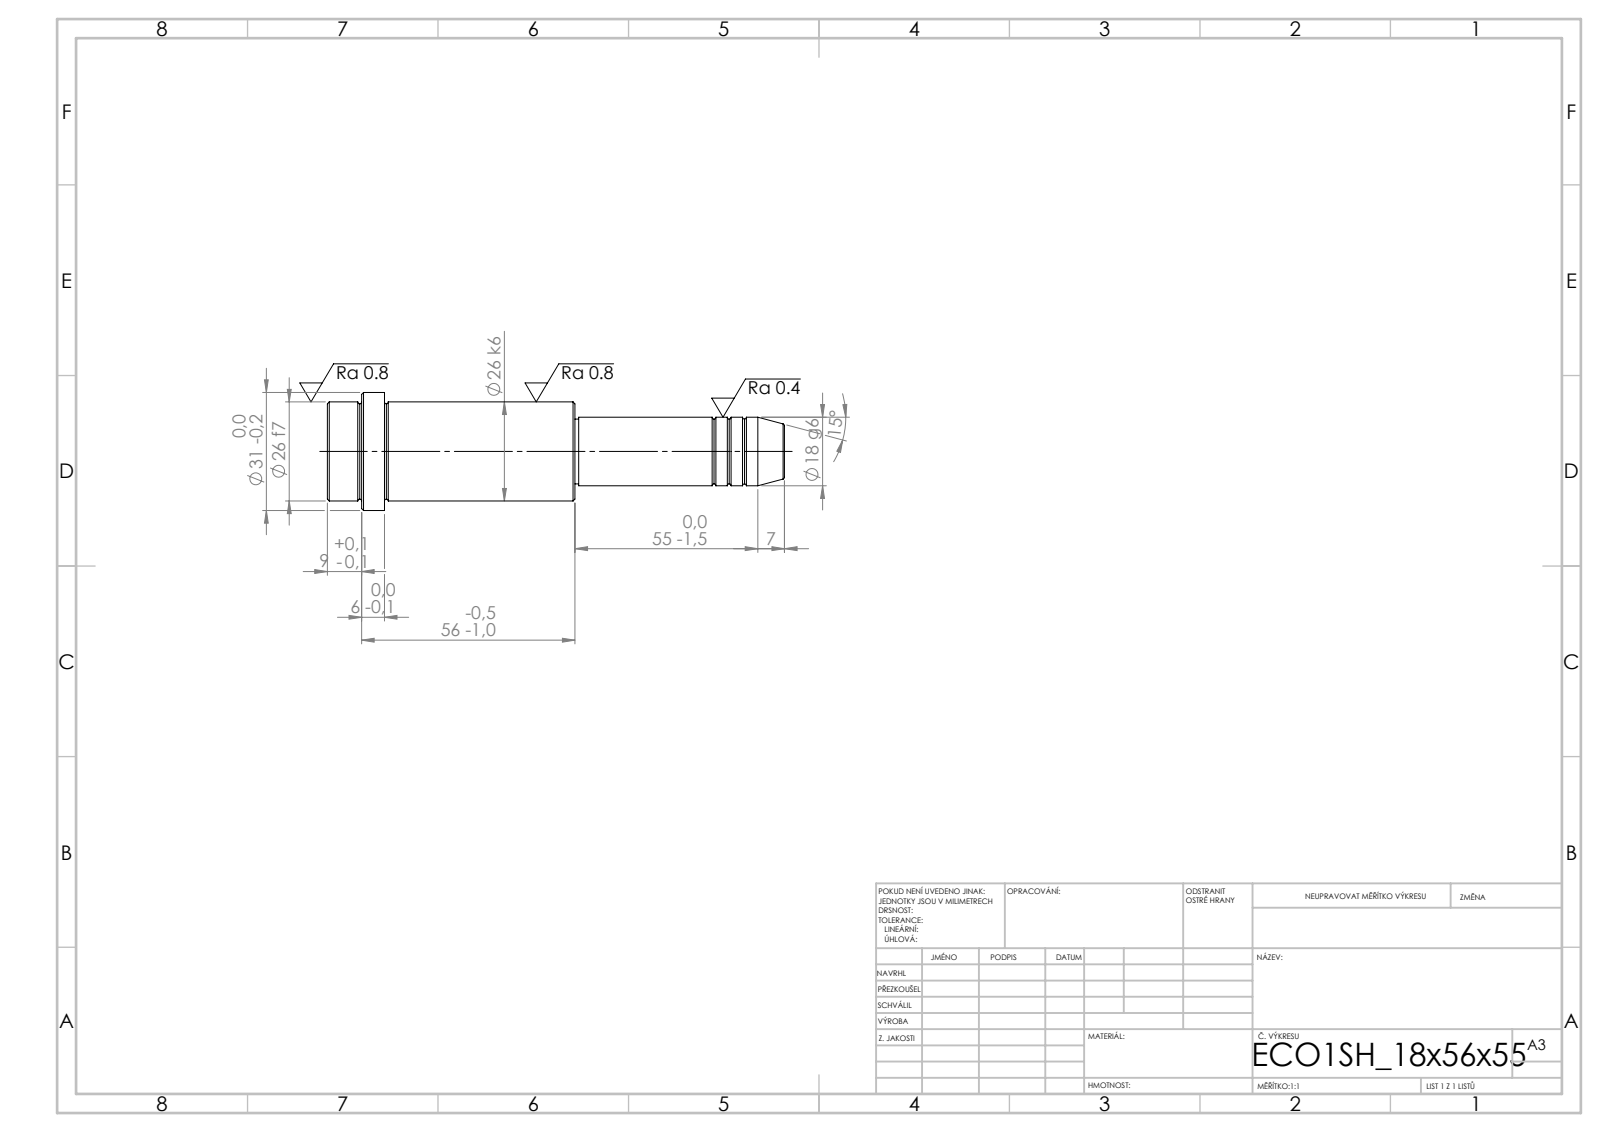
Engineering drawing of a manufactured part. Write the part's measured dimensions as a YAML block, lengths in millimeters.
step_written_by: "SolidWorks 2019 (CONFIG_CONTROL_DESIGN)"
units: millimeters
bodies: {solids: 1, faces: 52, planar: 6, cylindrical: 16, other: 30}
overall_size: [120, 31, 31]
volume: 49315
surface_area: 10043
round_bosses_or_shafts:
  - {diameter: 31, count: 1}
  - {diameter: 26, count: 1}
  - {diameter: 18, count: 1}
  - {diameter: 17, count: 1}
face_to_face_distances: [65, 50, 15, 56, 6, 9, 55, 105, 111, 120]
